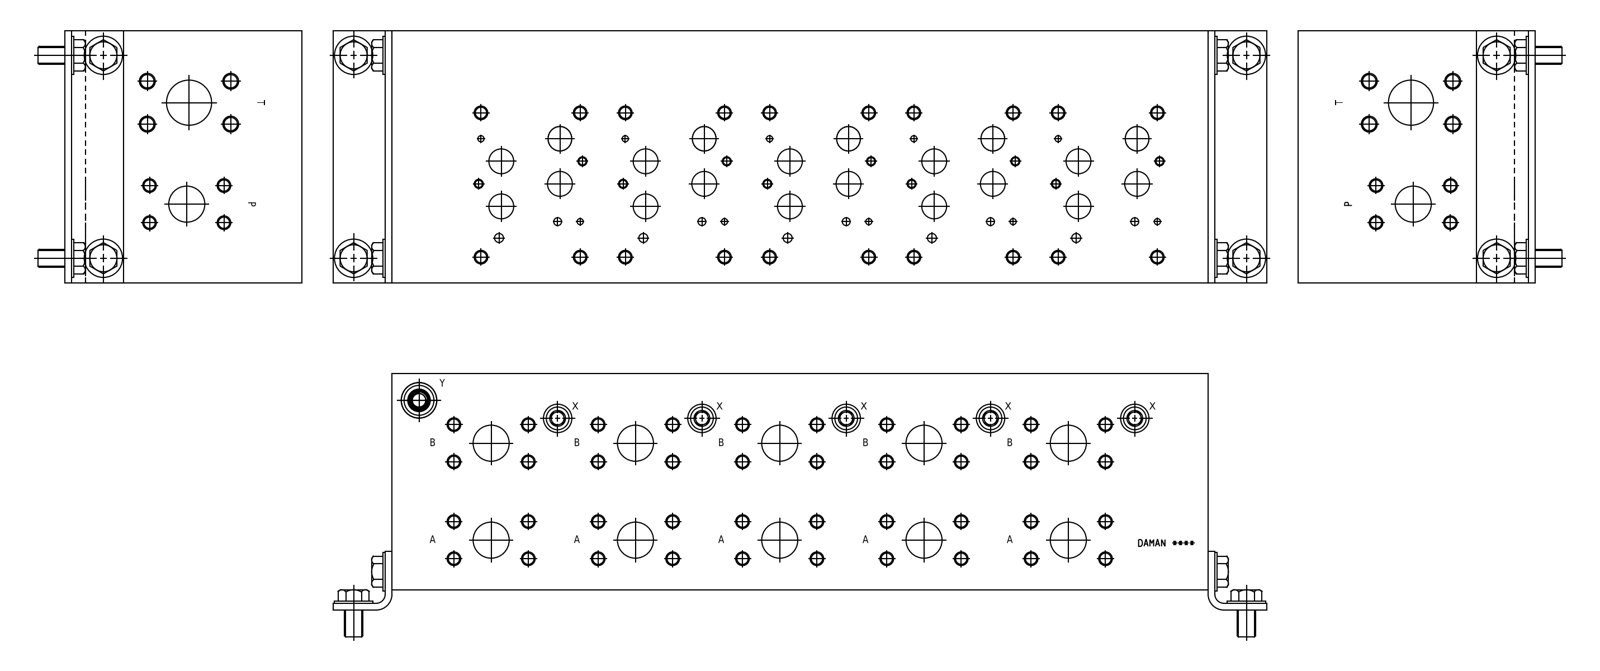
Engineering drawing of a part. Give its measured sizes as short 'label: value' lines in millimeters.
name: C:\\Program Files\\PARO\\Hydroman 800\\Export\\AD07HP054F_M1
written by: Autodesk Inventor 2012 (AUTOMOTIVE_DESIGN)
unit: mm
bodies: 1 solid, 342 faces (18 planar, 168 cylindrical, 156 other)
size: 574.67 × 177.8 × 152.4
volume: 15 310 000 mm³; area: 522 788 mm²
holes: 51× ⌀8.51, 20× ⌀8.51, 15× ⌀17.48, 11× ⌀25.4, 10× ⌀4.37, 10× ⌀5, 10× ⌀6.35, 5× ⌀5.56, 5× ⌀9.04, 5× ⌀11.1, 5× ⌀16.66, 5× ⌀19.99
face distances: 152.4, 177.8, 574.67, 0.79, 177.01, 2.39, 1.6, 175.41, 3.17, 2.38
hole spacings: 101.6, 122.4, 104.92, 128.46, 26.17, 29.27, 29.28, 52.38
